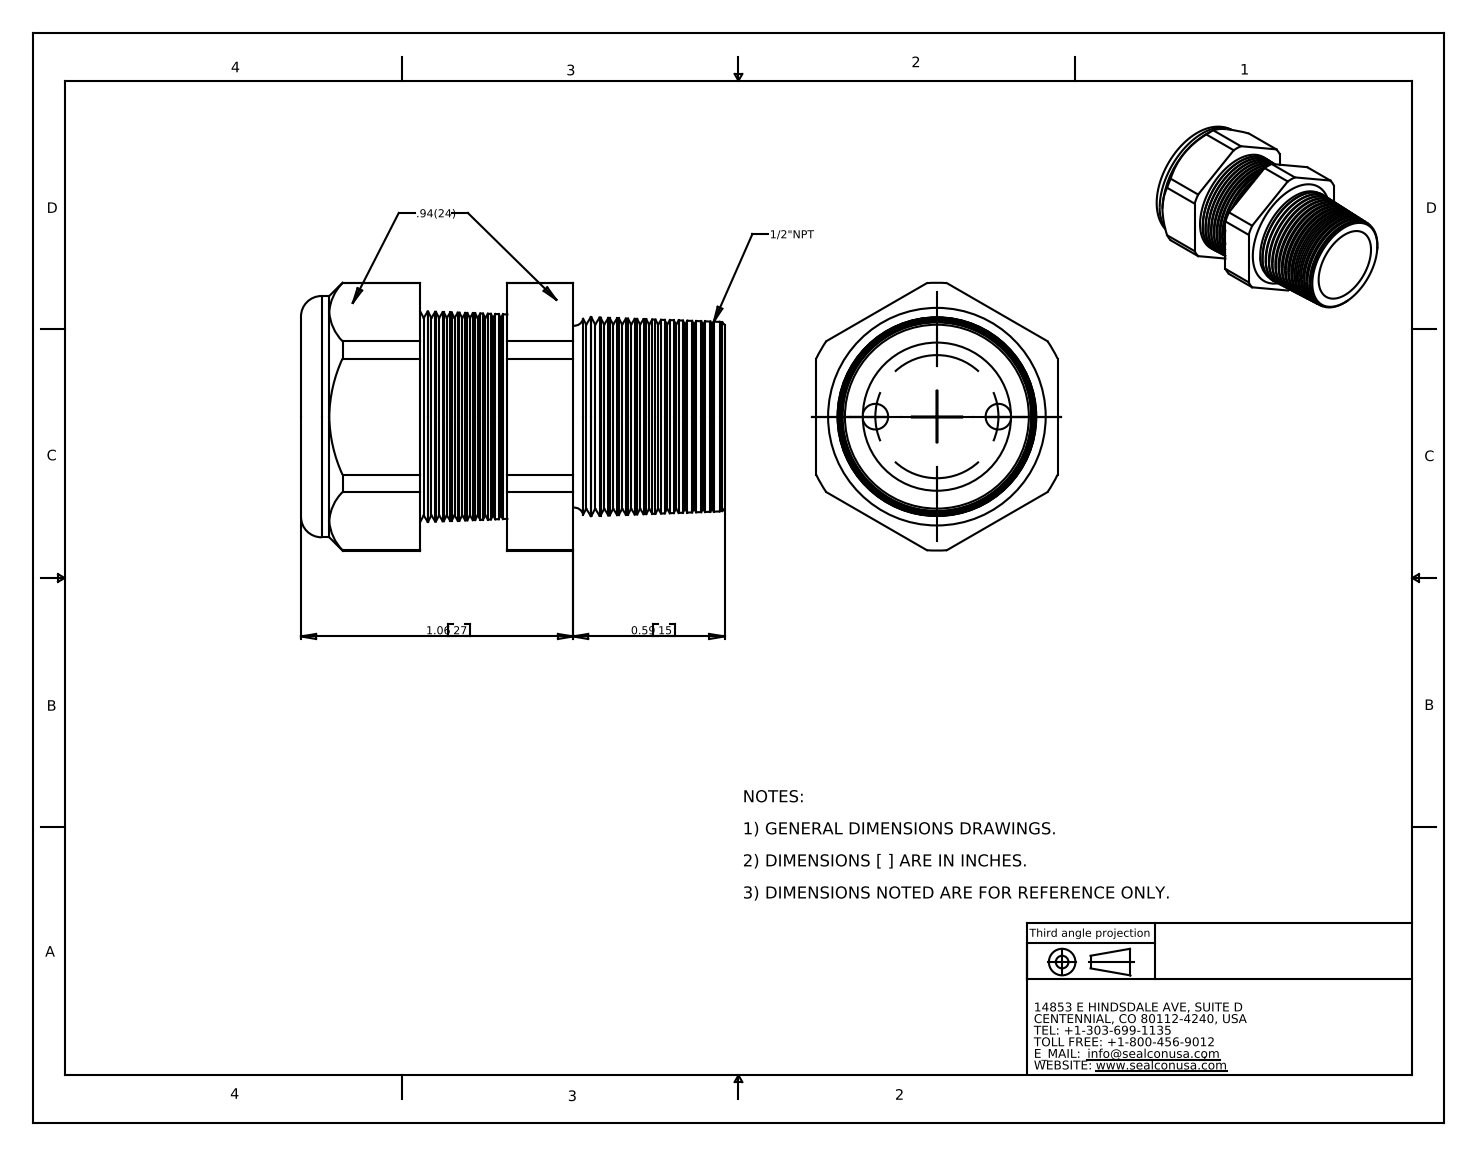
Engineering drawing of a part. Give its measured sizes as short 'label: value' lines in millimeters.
name: CD13N9-BK
written by: SolidWorks 2007 (CONFIG_CONTROL_DESIGN)
unit: mm
bodies: 2 solids, 220 faces (20 planar, 24 cylindrical, 176 other)
size: 41.9 × 26.5 × 23.9
volume: 9 640 mm³; area: 7 671 mm²
holes: 2× ⌀2.5, 1× ⌀14.7, 1× ⌀15.2
bosses: 1× ⌀23.9
rounds: 1× R13.3
face distances: 23.9, 11.5, 8.4, 19.9, 11.3, 2.9, 8.6, 0.5, 8.9, 11.8
hole spacings: 6.1, 12.2
